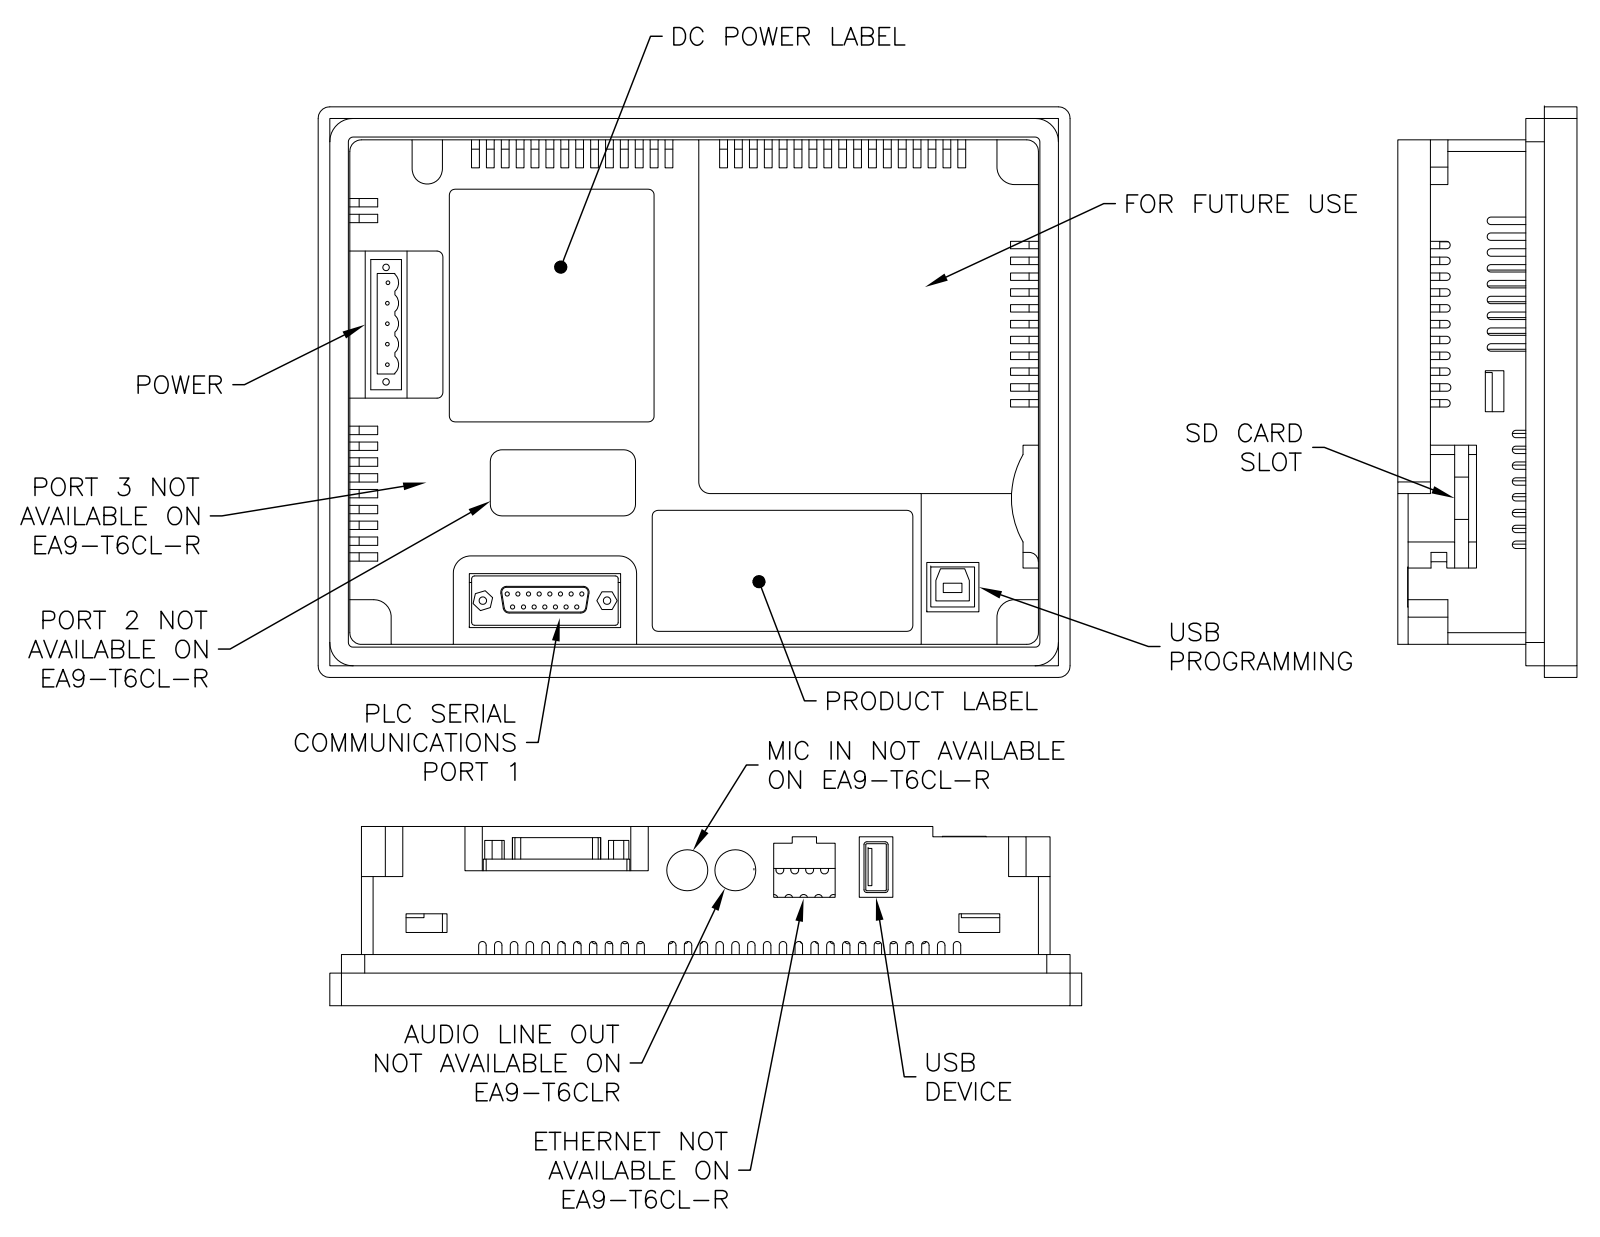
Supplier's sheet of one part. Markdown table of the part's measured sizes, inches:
| quantity | value |
| --- | --- |
| part name | EA9-T6CL-R |
| STEP written by | SolidWorks 2014 (AUTOMOTIVE_DESIGN) |
| units | inches |
| bodies | 5 solids, 1345 faces (708 planar, 598 cylindrical, 39 other) |
| overall size | 8.08 × 6.13 × 1.925 |
| volume | 16.68 in³ |
| surface area | 308.3 in² |
| round holes (diameter × count) | 0.045 × 14, 0.07 × 2, 0.08 × 2, 0.44 × 2, 0.045 × 1 |
| round bosses / shafts (diameter × count) | 0.04 × 5 |
| partial cylindrical surfaces (radius × count) | 0.04 × 203, 0.031 × 42, 0.042 × 33, 0.063 × 22, 0.062 × 14, 0.125 × 13, 0.045 × 11, 0.025 × 8 |
| main face-to-face distances | 0.1, 1.824, 0.35, 1.474, 5.32, 1.924, 0.25, 1.724, 0.45, 1.574 |
| hole center spacings | 0.115, 0.15, 0.152, 0.224, 0.229, 0.343, 0.458, 0.229 |
